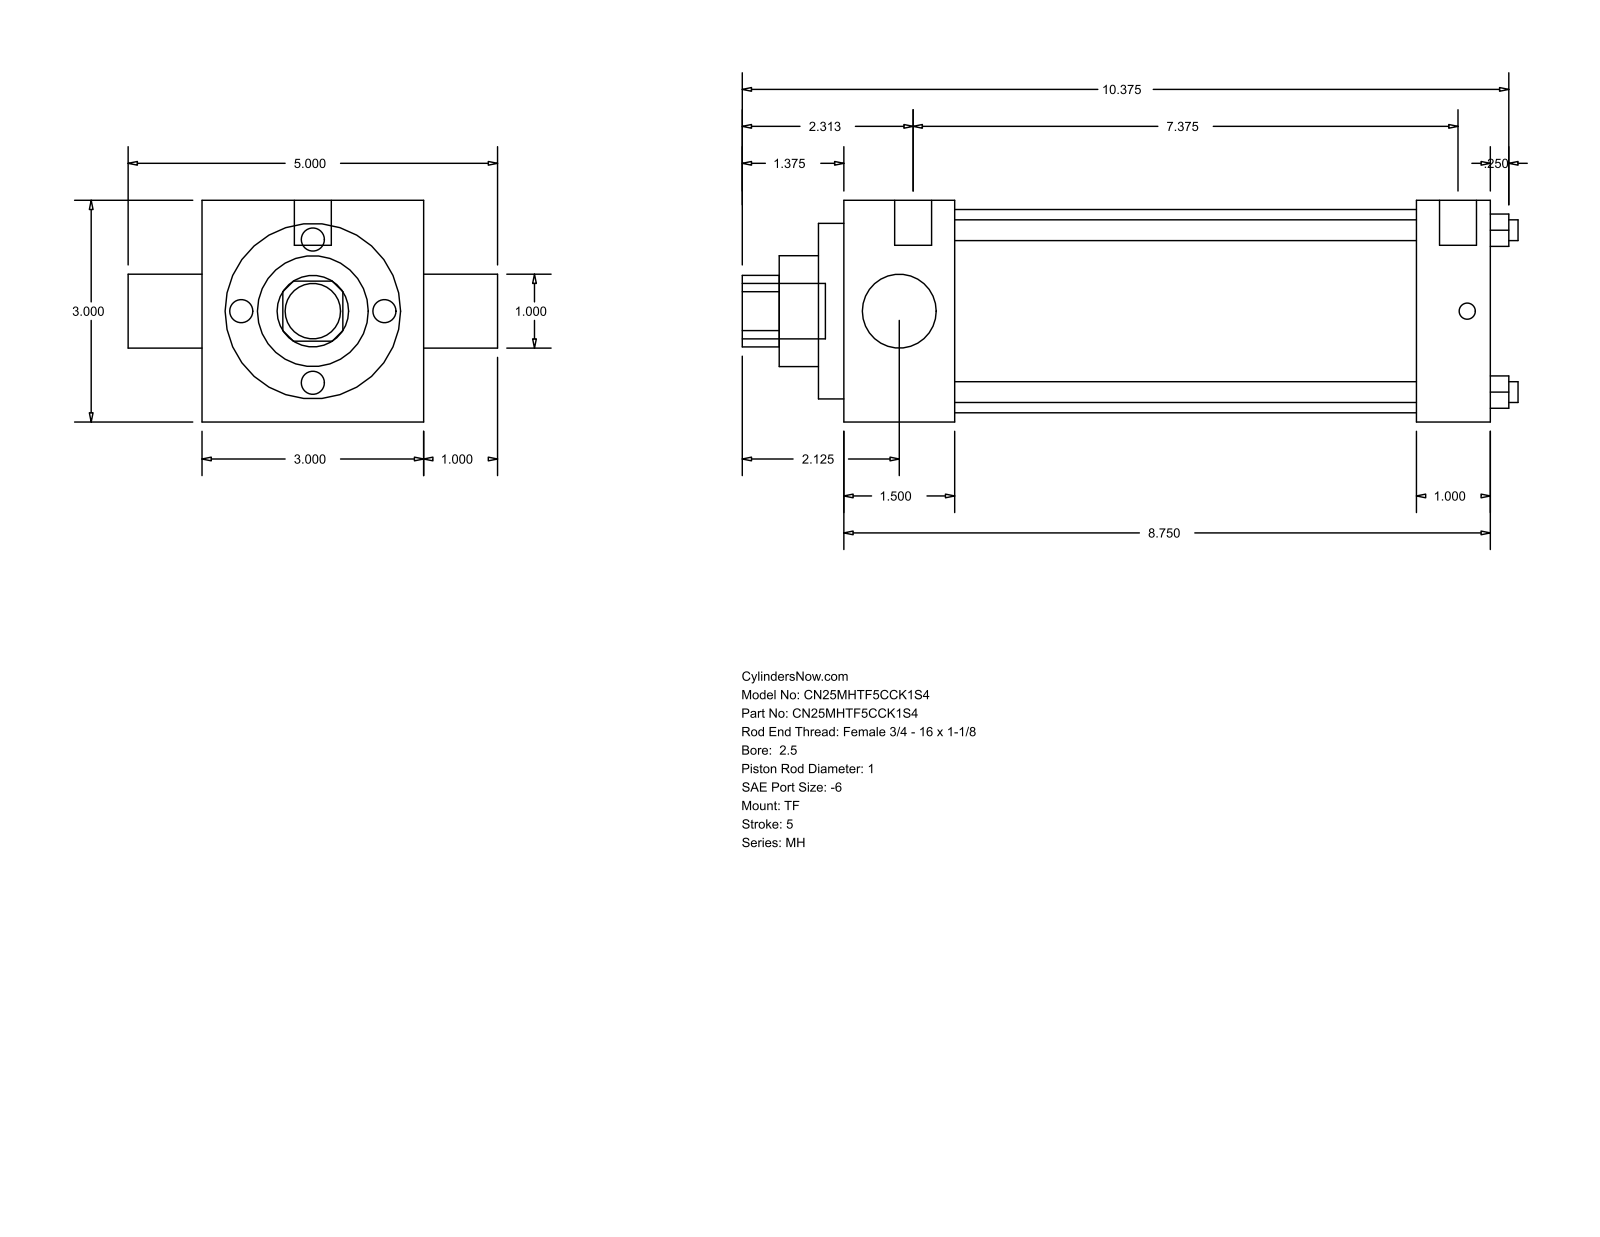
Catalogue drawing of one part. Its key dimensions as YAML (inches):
part_name: "MH_TF__0250_1"
step_written_by: "GSSL Pune (CONFIG_CONTROL_DESIGN)"
units: inches
bodies: {solids: 0, faces: 86, planar: 61, cylindrical: 25, other: 0}
overall_size: [10.5, 5, 3]
round_holes:
  - {diameter: 0.281, count: 4}
  - {diameter: 1, count: 2}
  - {diameter: 1.5, count: 1}
  - {diameter: 2.375, count: 1}
  - {diameter: 2.75, count: 1}
round_bosses_or_shafts:
  - {diameter: 0.219, count: 3}
  - {diameter: 0.5, count: 2}
  - {diameter: 0.75, count: 1}
partial_cylinders:
  - {radius: 0.484, count: 1}
face_to_face_distances: [3, 8.75, 1, 1.5, 7.25, 7.75, 6.25, 0.344, 1.844, 8.094]
hole_center_spacings: [1.548, 2.19, 3.097]
